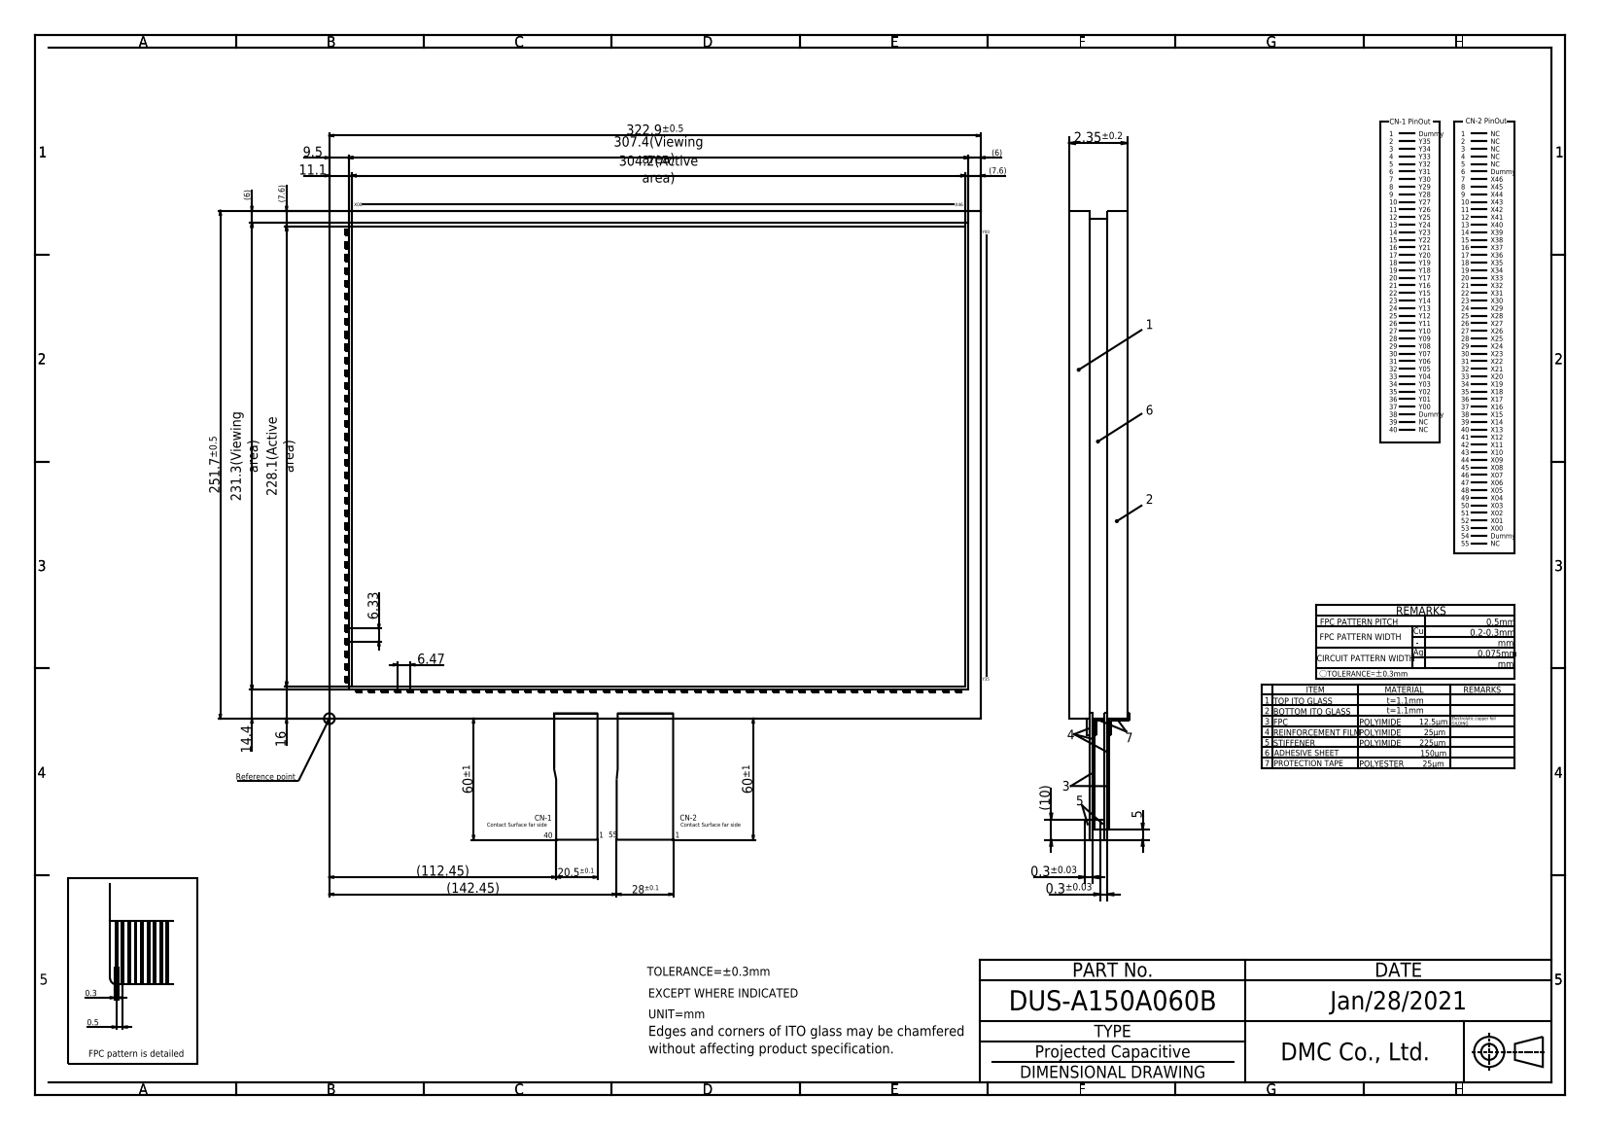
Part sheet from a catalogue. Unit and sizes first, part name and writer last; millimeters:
Units: millimetres
Overall size (bounding box): 452.06 × 362.04 × 2.35
Partial cylindrical surfaces — rounded edges, fillets, slot ends (radius × count): R0.2 ×4
Main face-to-face distances: 2.35, 1.1, 1.15, 1.2, 1.25, 1, 2.25, 251.7, 322.9, 0.8
Volume: 191 235 mm³ · Surface area: 171 382 mm²
Bodies: 1 solid, 422 faces (418 planar, 4 cylindrical, 0 other)
Part name (STEP PRODUCT): DUS-A150A060B
STEP written by: Autodesk Inventor 2020 (CONFIG_CONTROL_DESIGN)
